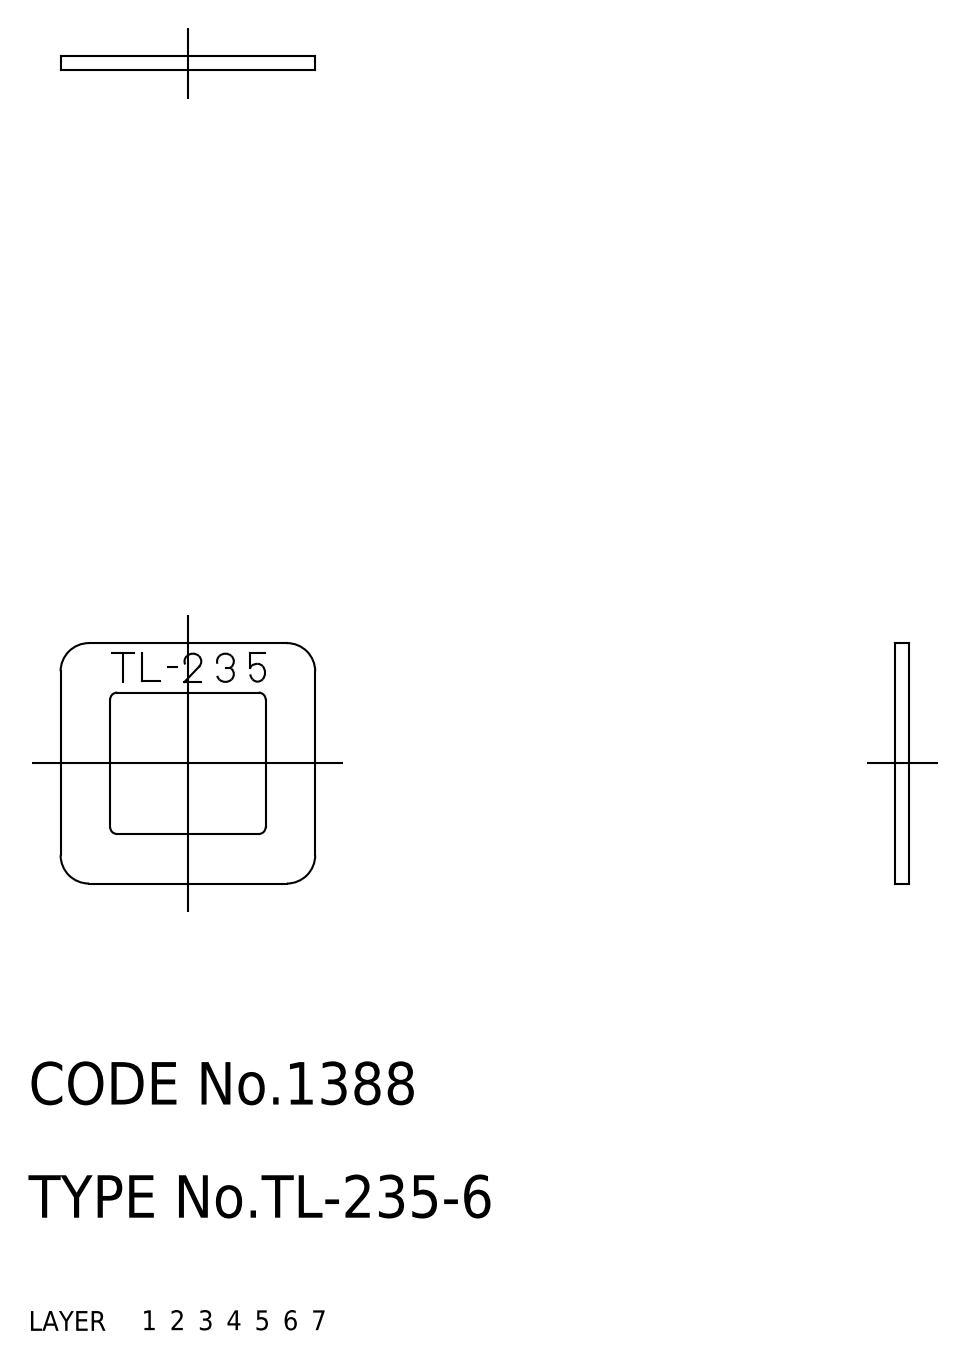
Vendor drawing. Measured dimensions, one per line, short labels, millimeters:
name: spacer
written by: CADfix (AUTOMOTIVE_DESIGN)
unit: mm
bodies: 1 solid, 18 faces (0 planar, 0 cylindrical, 18 other)
size: 18 × 17 × 1
volume: 193 mm³; area: 493 mm²
